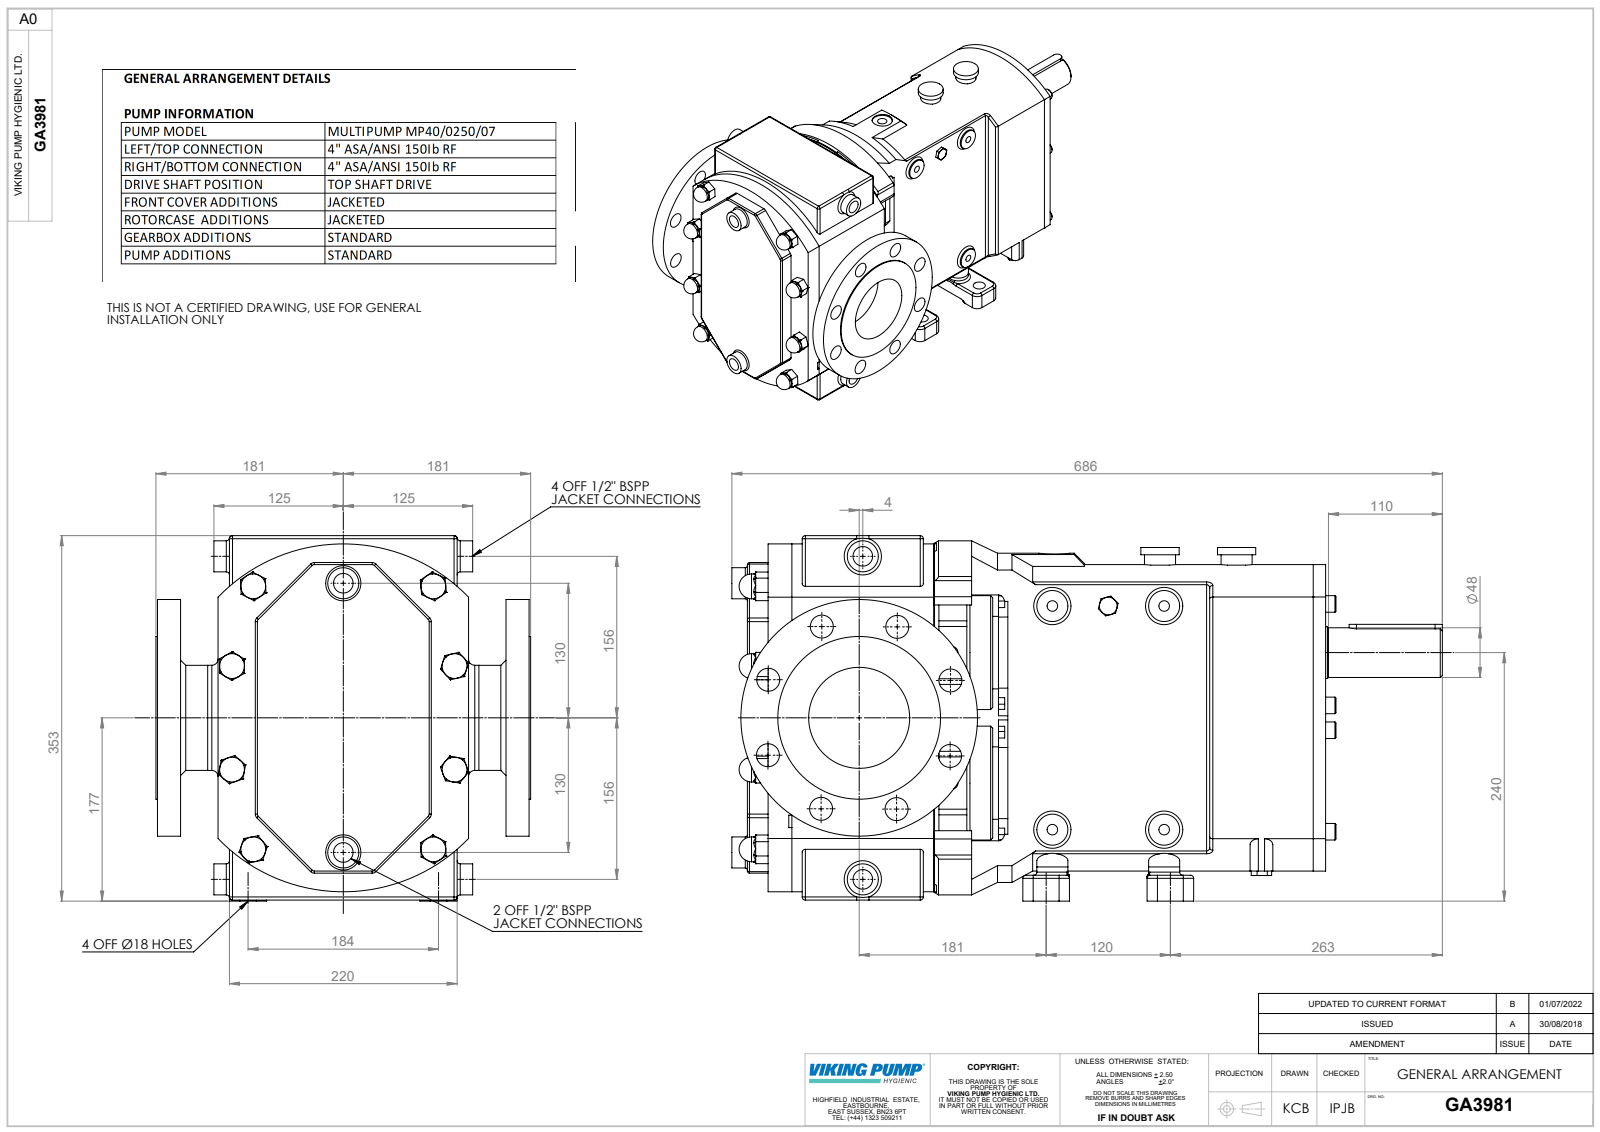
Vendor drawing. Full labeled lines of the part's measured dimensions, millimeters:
Part name (STEP PRODUCT): Copy of CP-MP40L Jacket Rotorcase^GA3981; Copy of CP40L-0250 H TSD^GA3981; Copy of Z94-5301-66 - 4 INCH ASA 150^GA3981; Copy of CP-MP40 Jacket Front Cover^GA3981 (+1 more)
STEP written by: SolidWorks 2023 (AUTOMOTIVE_DESIGN)
Units: millimetres
Bodies: 6 solids, 1105 faces (395 planar, 369 cylindrical, 341 other)
Overall size (bounding box): 686.37 × 362 × 353
Volume: 32 100 000 mm³ · Surface area: 1 392 000 mm²
Round holes (diameter × count): ⌀22.2 ×16, ⌀10.2 ×4, ⌀18 ×4, ⌀18.97 ×4, ⌀11.89 ×2, ⌀35 ×2, ⌀13.83 ×1, ⌀30 ×1, ⌀97.6 ×1
Round bosses / shafts (diameter × count): ⌀30 ×14, ⌀24 ×8, ⌀16 ×6, ⌀110 ×2, ⌀70 ×2, ⌀37 ×2, ⌀31.75 ×2, ⌀250 ×1
Partial cylindrical surfaces — rounded edges, fillets, slot ends (radius × count): R3 ×34, R10 ×24, R8 ×20, R5 ×12, R6 ×10, R2 ×8, R11 ×4, R7 ×2
Main face-to-face distances: 21, 212, 87.2, 227.2, 36.2, 278.2, 51, 191, 66.2, 248.2
Hole centre spacings: 190.5, 72.9, 176, 95.25, 72.2, 134.7, 134.71, 176.29
